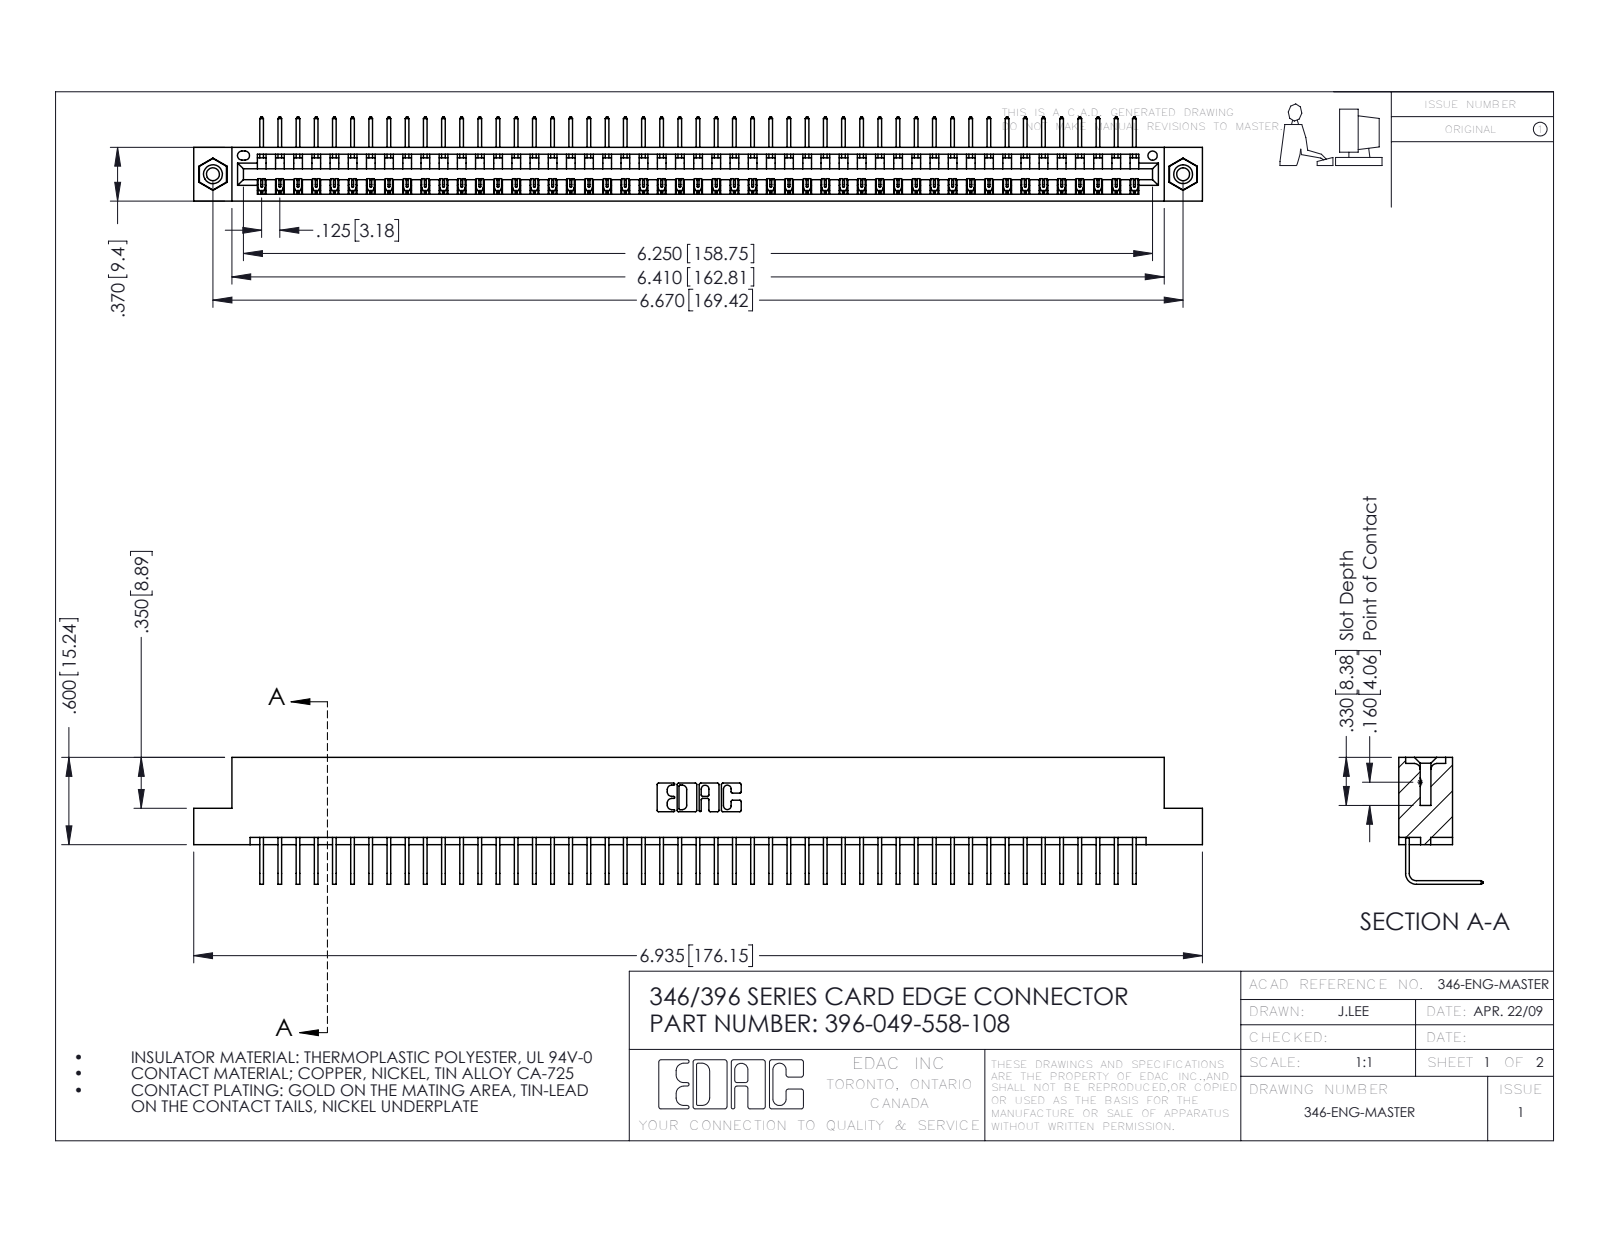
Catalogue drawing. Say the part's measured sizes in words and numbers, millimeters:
The part is named "345-292-001_558 Tail - 2; 346 Part_Flush Mounting Lugs - 0.156 Dia-TI; 396-049-558-108; 345-250-001_345-250-003-102". Its 3-D file was written by "SolidWorks 2016 (CONFIG_CONTROL_DESIGN)". It is 52 solids with 3122 faces: 2166 planar, 940 cylindrical and 16 other. Overall it measures 176.1 by 22.2 by 14.7 millimeters. Its volume is 17 060 cubic millimeters and its surface area 22 400 square millimeters. Round holes: 2 of diameter 2.3, 2 of diameter 3.2, 2 of diameter 4, 1 of diameter 1.6. Round bosses or shafts: 2 of diameter 3.9. Partial cylindrical surfaces (rounded edges, fillets, slot ends): 98 of radius 0.2, 22 of radius 0.3, 6 of radius 0.2, 6 of radius 0.8, 3 of radius 0.7, 2 of radius 0.8, 2 of radius 1, 1 of radius 0.4. The main face-to-face distances are 8.2, 1.2, 9.4, 6.4, 7.6, 0.6, 1.8, 3.8, 5.6, 2.5. The hole center spacings are 6.2, 164.1, 169.4.
